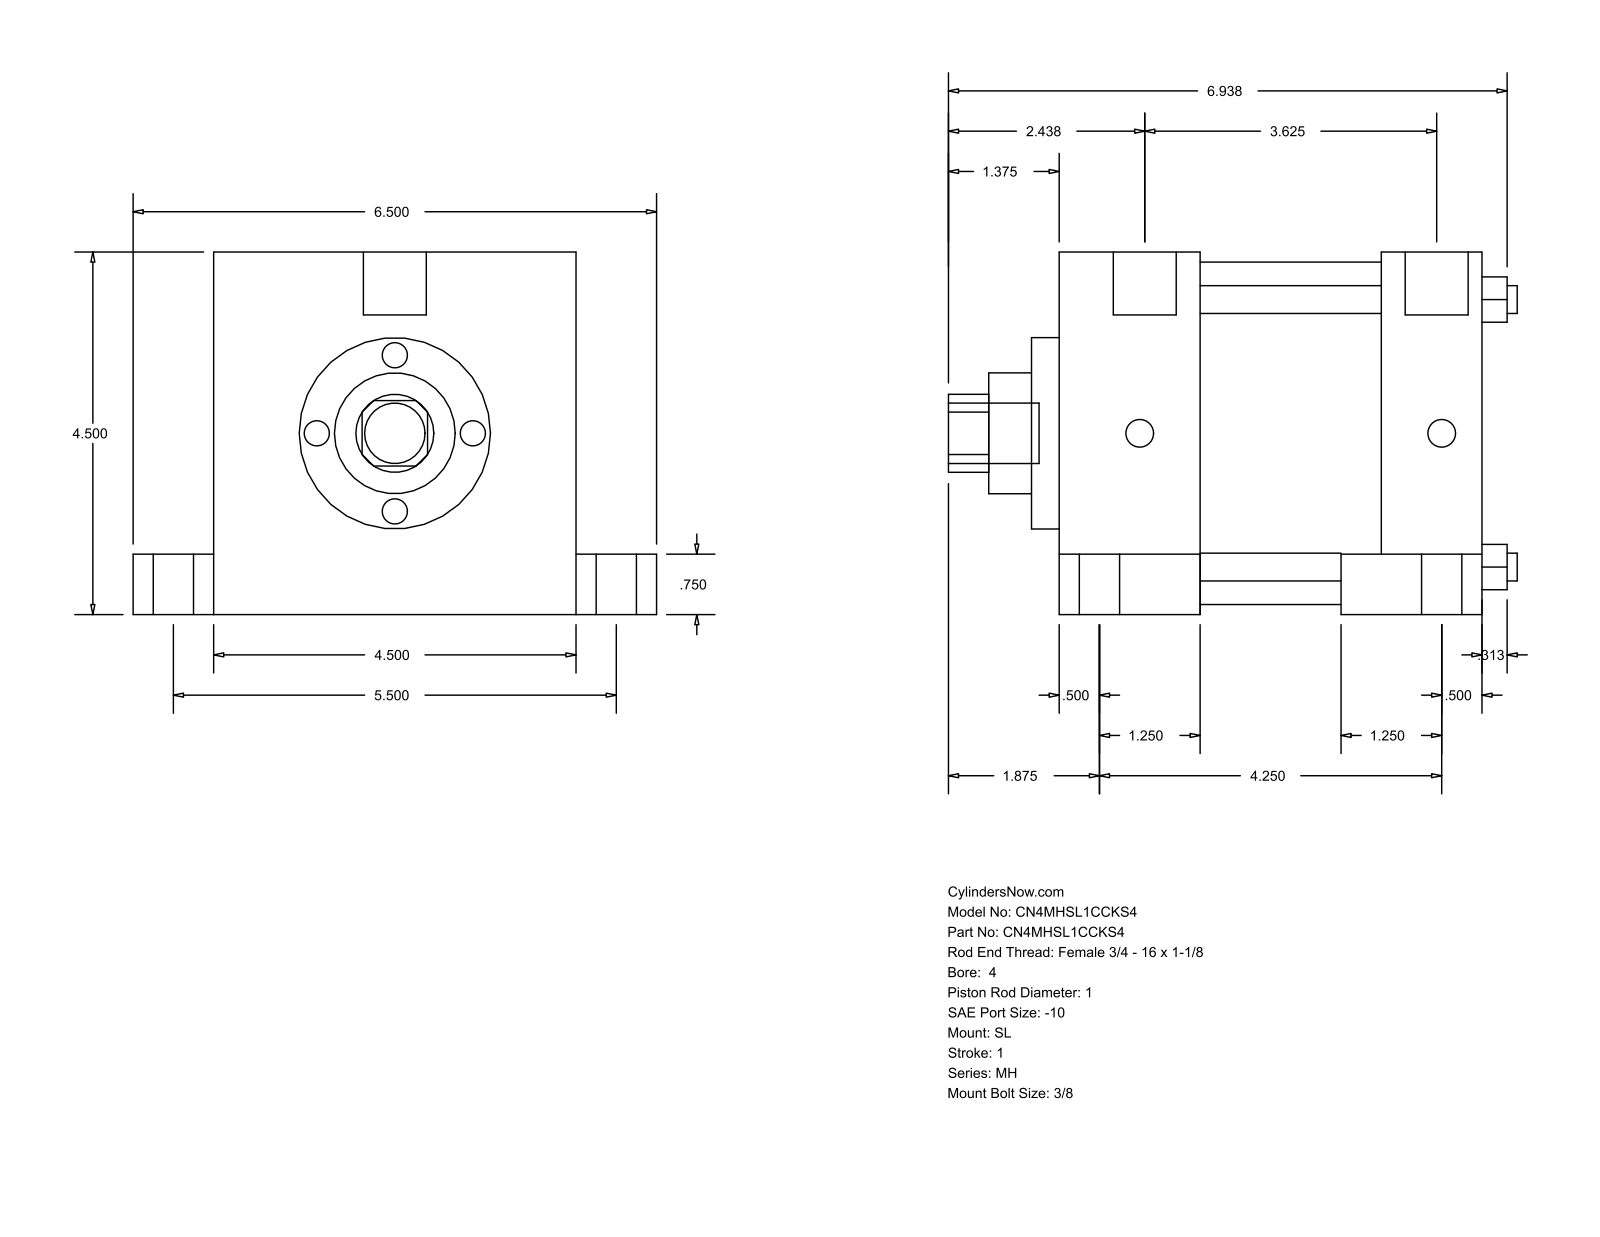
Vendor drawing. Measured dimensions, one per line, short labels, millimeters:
name: MH_SL__0400_1
written by: GSSL Pune (CONFIG_CONTROL_DESIGN)
unit: mm
bodies: 0 solids, 110 faces (77 planar, 33 cylindrical, 0 other)
size: 179.39 × 165.1 × 114.3
holes: 4× ⌀8.76, 1× ⌀25.4, 1× ⌀38.1, 1× ⌀60.33, 1× ⌀107.95
bosses: 5× ⌀19.05, 4× ⌀12.7, 4× ⌀8.73, 2× ⌀19.84
rounds: 1× R12.29
face distances: 114.3, 133.36, 44.46, 88.9, 101.61, 57.15, 31.75, 25.4, 139.7, 19.05
hole spacings: 59.62, 84.32, 119.25
